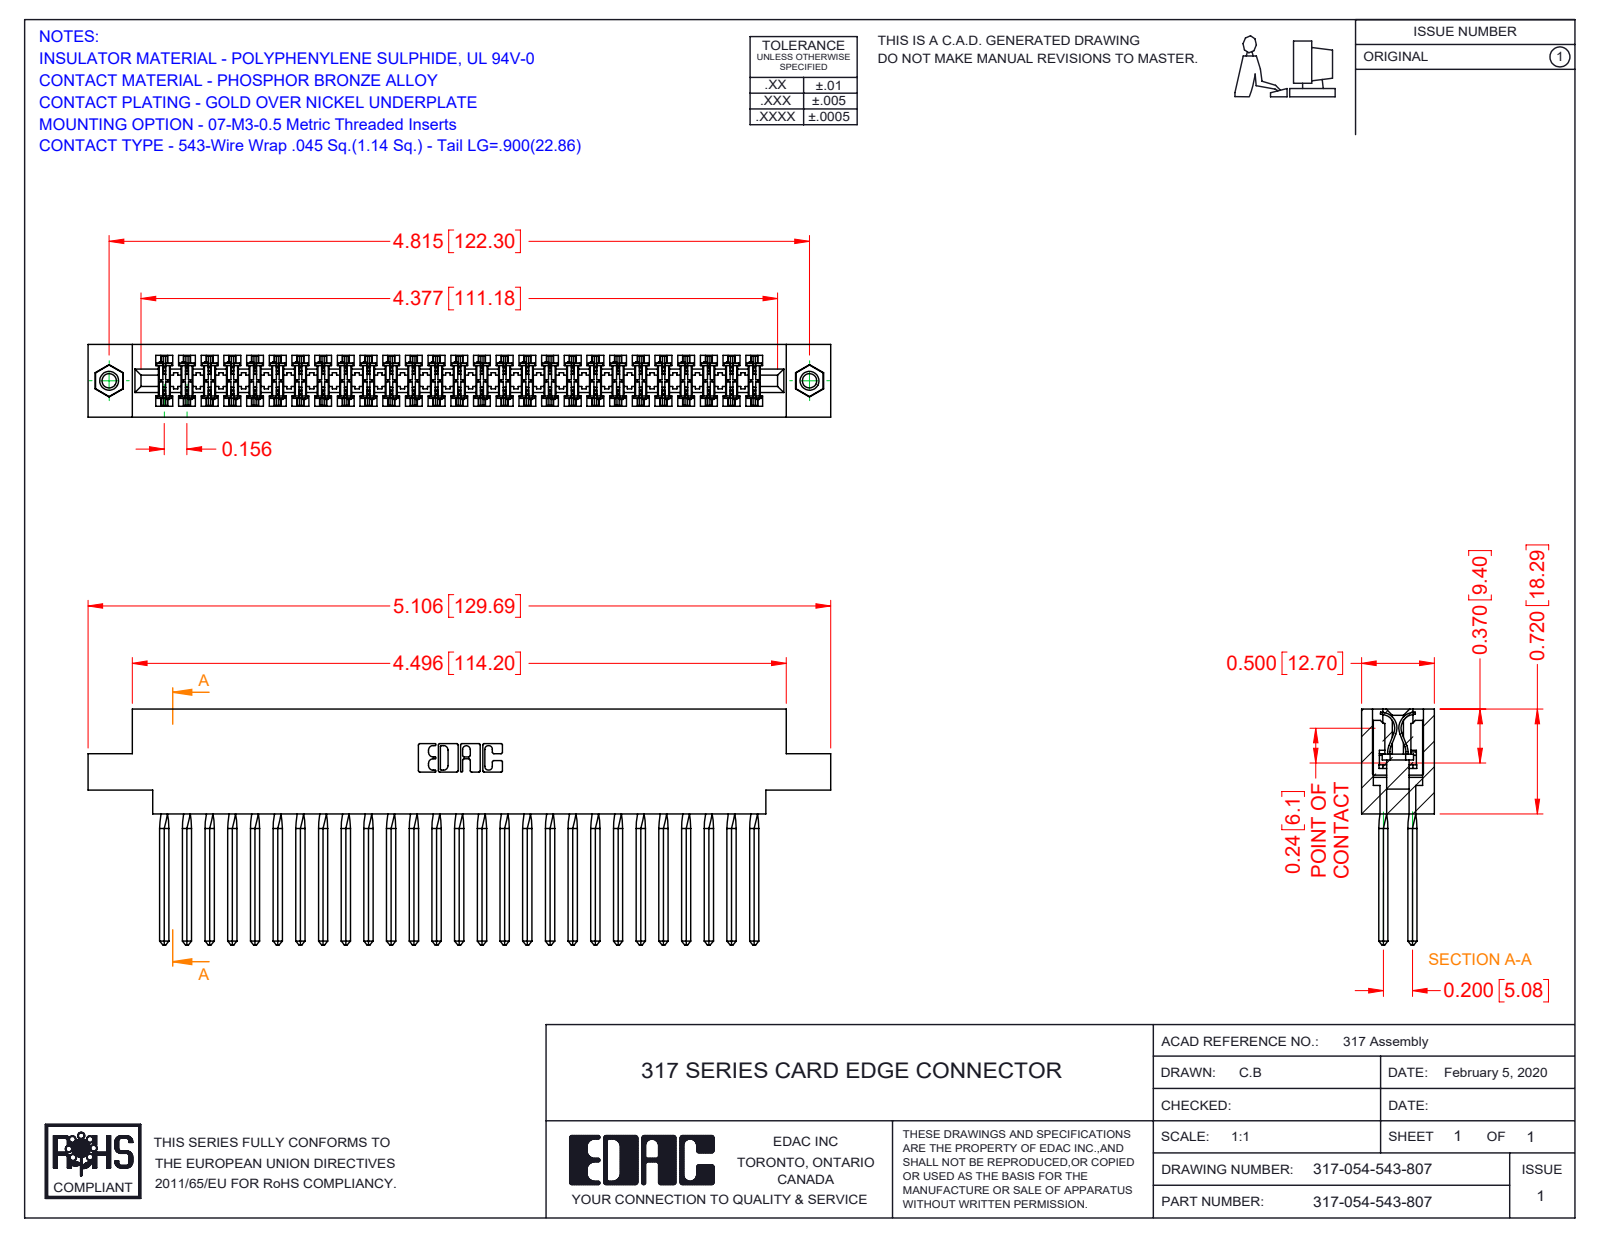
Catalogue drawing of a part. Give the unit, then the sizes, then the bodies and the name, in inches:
Units: inches
Overall size (bounding box): 5.106 × 1.62 × 0.5
Round holes (diameter × count): ⌀0.098 ×2, ⌀0.125 ×2, ⌀0.156 ×2
Round bosses / shafts (diameter × count): ⌀0.155 ×2
Partial cylindrical surfaces — rounded edges, fillets, slot ends (radius × count): R0.015 ×108, R0.01 ×22, R0.007 ×6, R0.031 ×6, R0.026 ×3, R0.095 ×2, R0.1 ×2, R0.11 ×2
Main face-to-face distances: 0.5, 0.075, 0.425, 0.35, 0.11, 0.195, 0.094, 0.2, 0.72, 0.115
Hole centre spacings: 4.815
Volume: 1.313 in³ · Surface area: 49.73 in²
Bodies: 57 solids, 4968 faces (4032 planar, 704 cylindrical, 232 other)
Part name (STEP PRODUCT): 317 Part_.156 Dia - TI; 345-250-001_345-250-005-103; 317-290-001_543; 317-054-543-807
STEP written by: SolidWorks 2016 (CONFIG_CONTROL_DESIGN)
